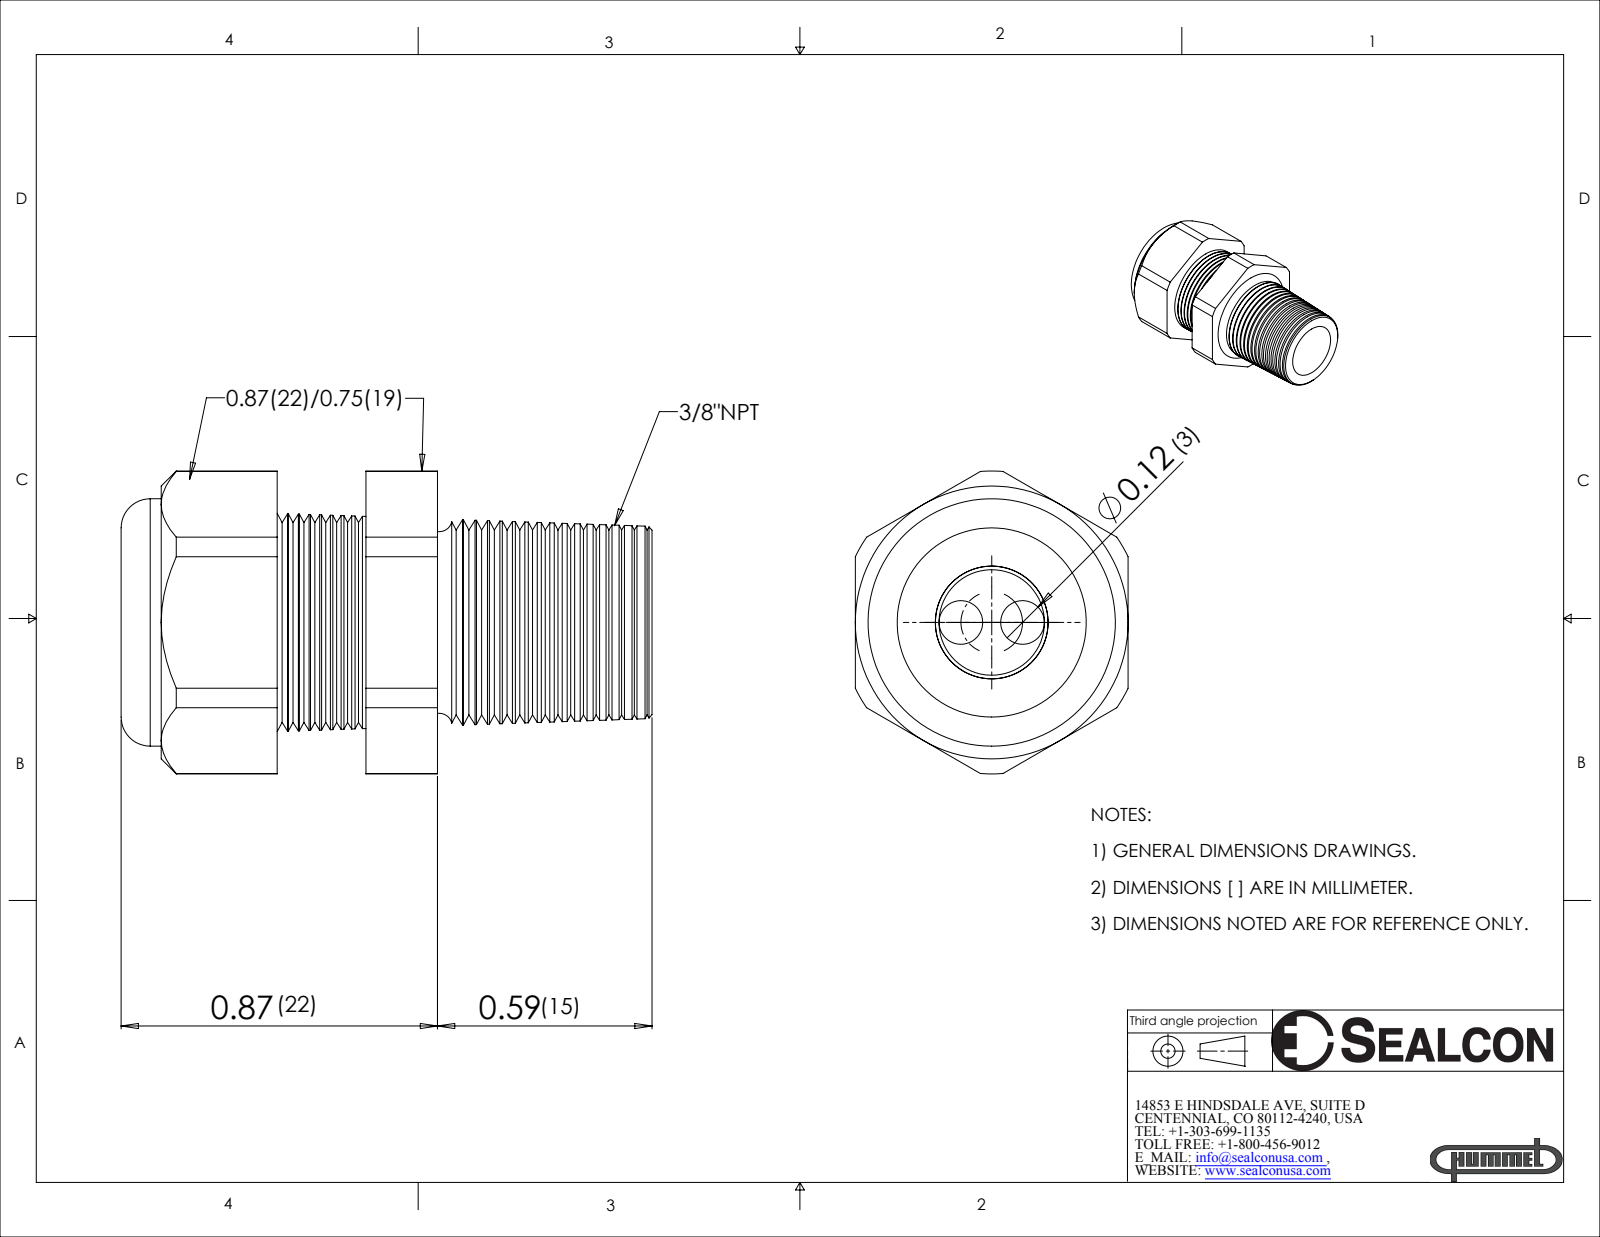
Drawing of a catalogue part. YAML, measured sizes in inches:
part_name: "CD09N2-BK"
step_written_by: "SolidWorks 2009 (CONFIG_CONTROL_DESIGN)"
units: inches
bodies: {solids: 2, faces: 203, planar: 21, cylindrical: 24, other: 158}
overall_size: [1.46, 0.833, 0.75]
volume: 0.359
surface_area: 6.993
round_holes:
  - {diameter: 0.12, count: 2}
  - {diameter: 0.29, count: 1}
  - {diameter: 0.31, count: 1}
round_bosses_or_shafts:
  - {diameter: 0.68, count: 1}
partial_cylinders:
  - {radius: 0.416, count: 1}
face_to_face_distances: [0.75, 0.244, 0.75, 0.441, 0.197, 0.429, 0.673, 0.87, 1.46, 1.031]
hole_center_spacings: [0.085, 0.169]
